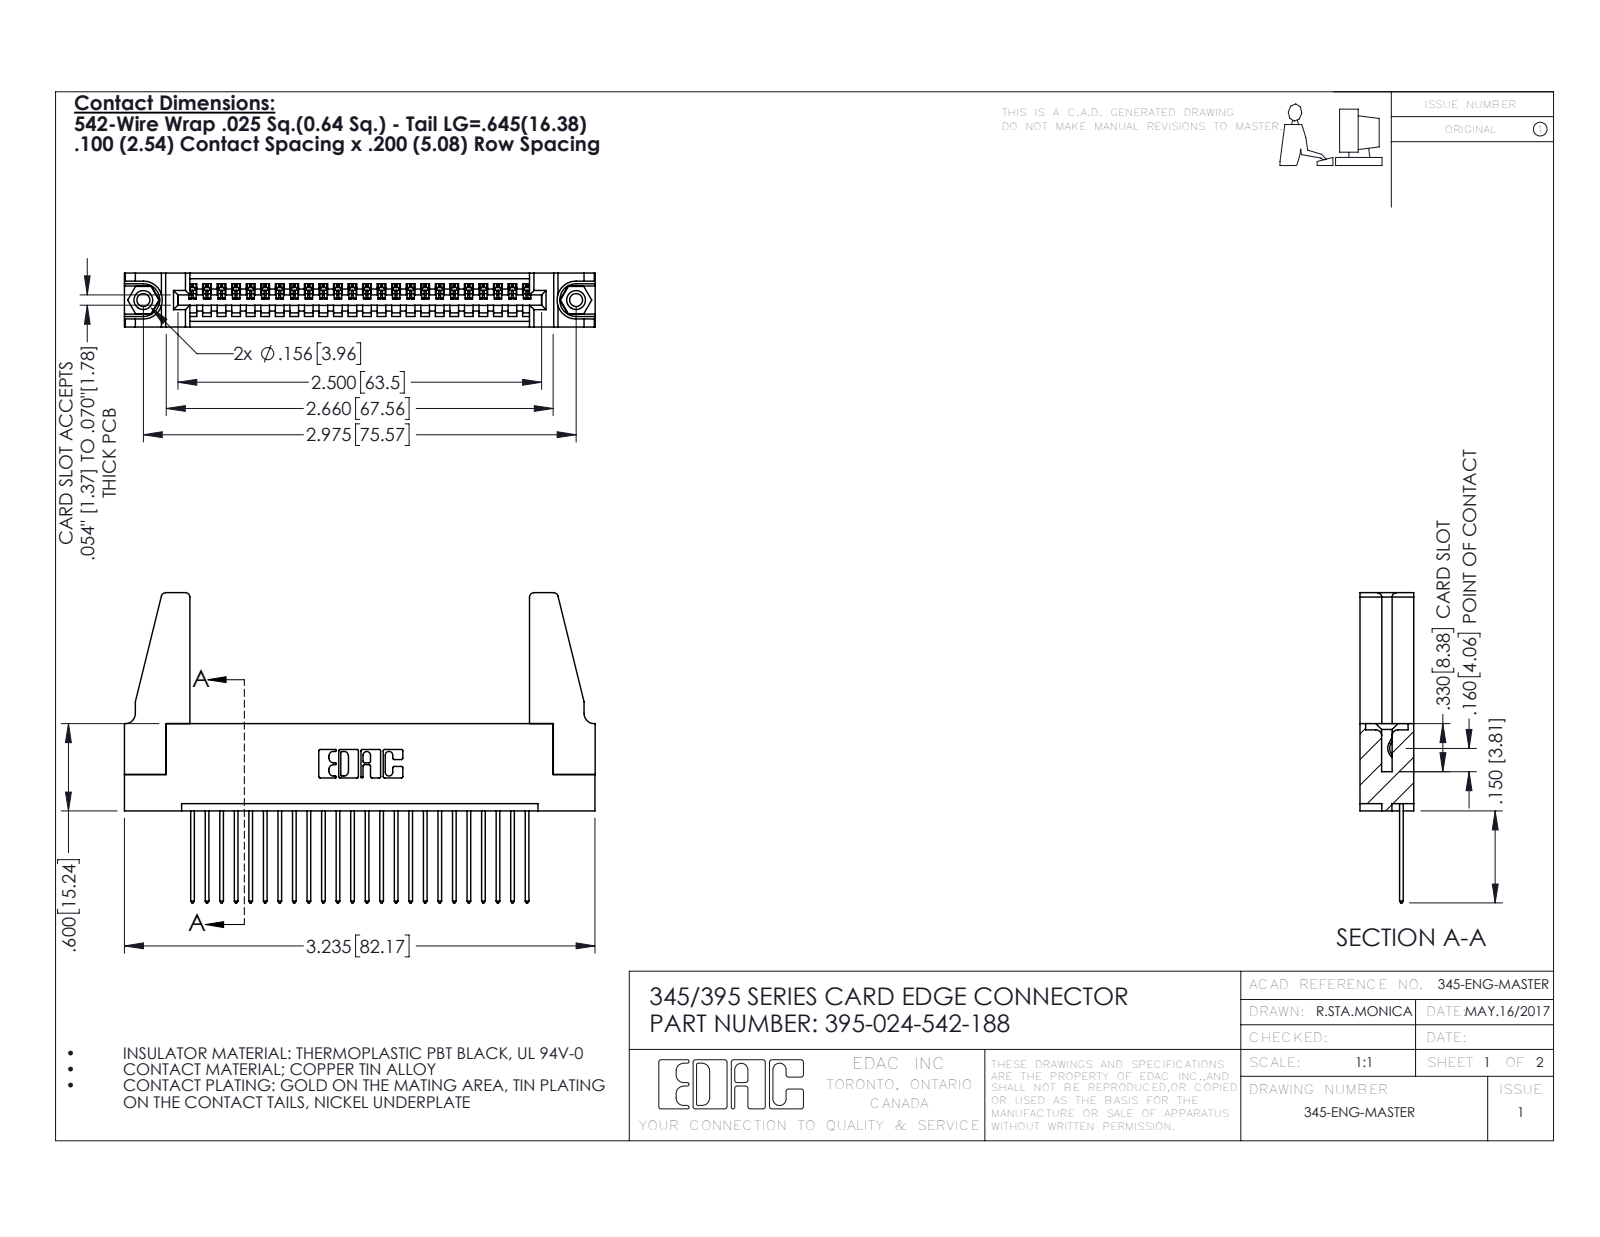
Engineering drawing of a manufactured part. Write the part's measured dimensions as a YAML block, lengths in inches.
part_name: "345 Part_Flush Mounting Lugs - 0.156 Dia-TH; 345-220-078_345-220-088; 345-292-001_345-293-142; 345-250-001_345-250-001-102 (+1 more)"
step_written_by: "SolidWorks 2016 (CONFIG_CONTROL_DESIGN)"
units: inches
bodies: {solids: 29, faces: 1642, planar: 1112, cylindrical: 514, other: 16}
overall_size: [3.236, 2.132, 0.37]
volume: 0.669
surface_area: 20.88
round_holes:
  - {diameter: 0.089, count: 2}
  - {diameter: 0.125, count: 2}
  - {diameter: 0.156, count: 2}
  - {diameter: 0.064, count: 1}
round_bosses_or_shafts:
  - {diameter: 0.155, count: 2}
partial_cylinders:
  - {radius: 0.006, count: 48}
  - {radius: 0.01, count: 48}
  - {radius: 0.01, count: 22}
  - {radius: 0.03, count: 8}
  - {radius: 0.007, count: 6}
  - {radius: 0.031, count: 6}
  - {radius: 0.026, count: 3}
  - {radius: 0.031, count: 2}
face_to_face_distances: [0.072, 0.298, 0.37, 0.2, 0.098, 0.272, 0.025, 0.225, 0.149, 0.148]
hole_center_spacings: [0.27, 2.741, 2.975]
